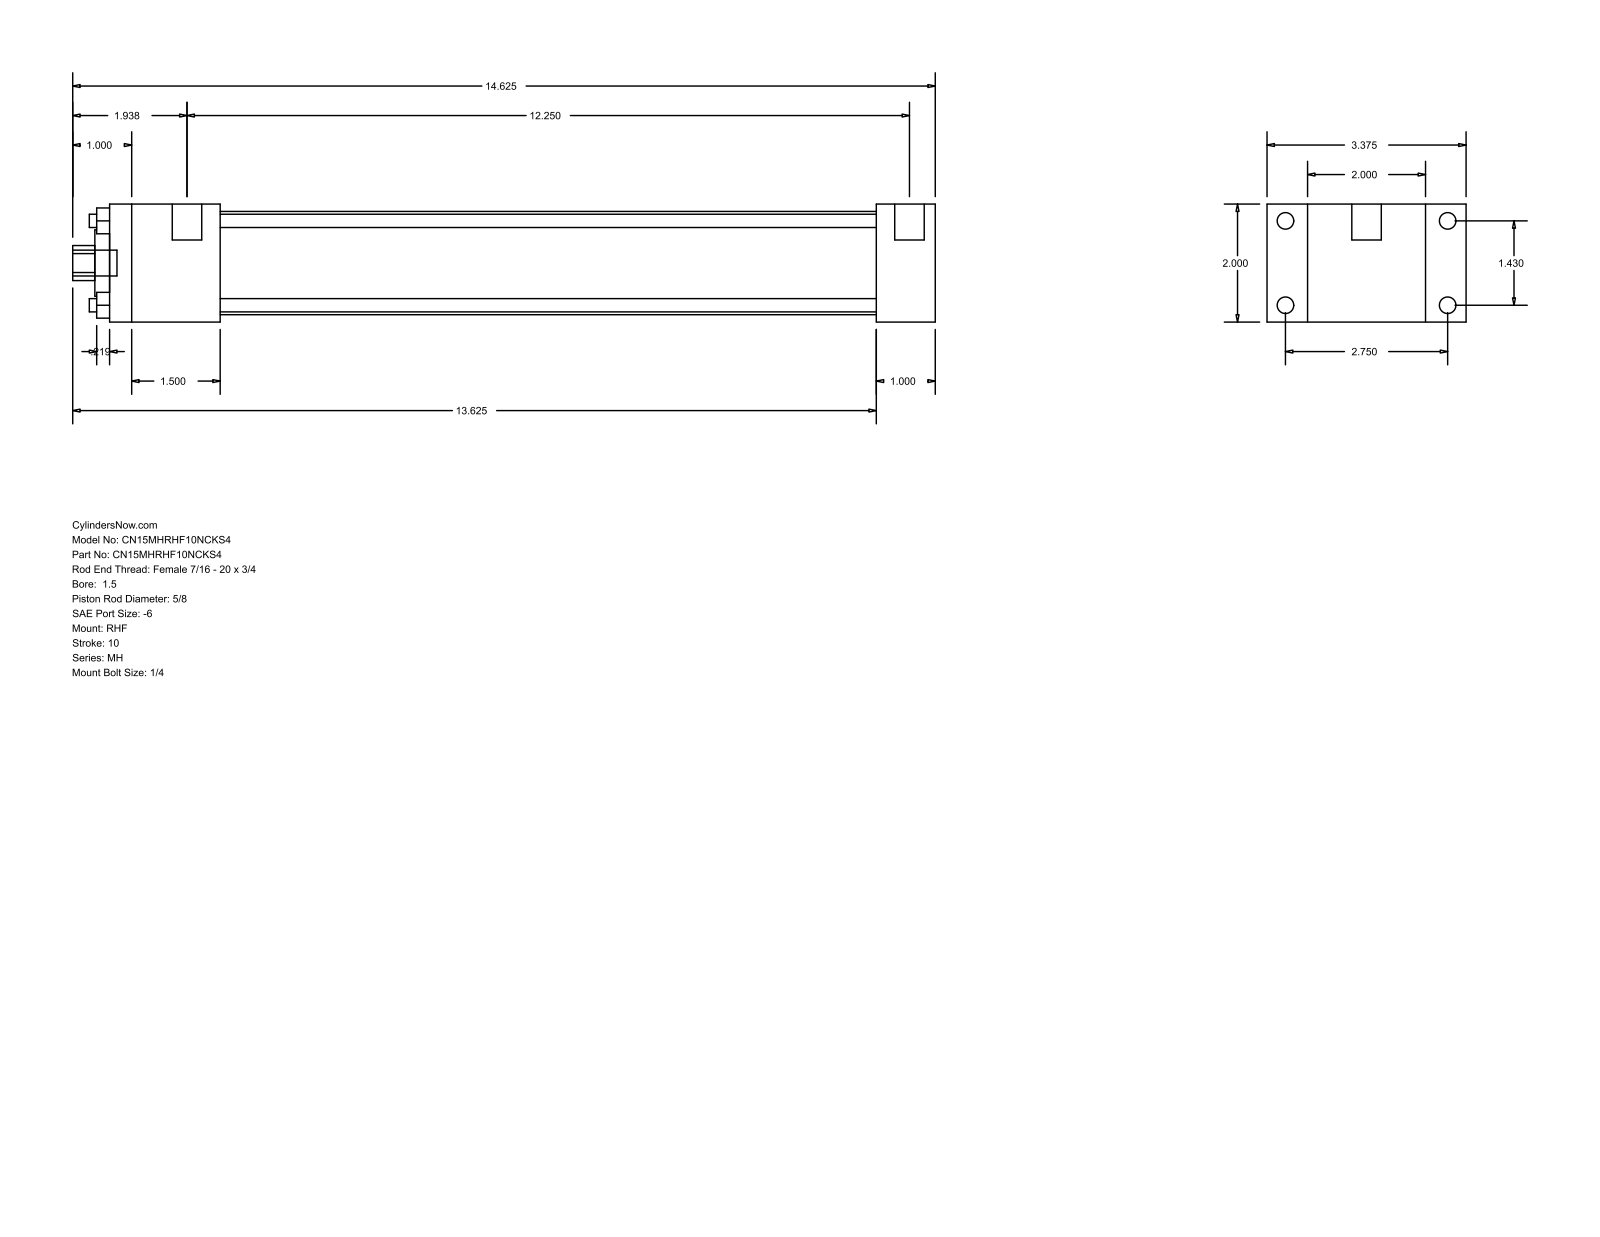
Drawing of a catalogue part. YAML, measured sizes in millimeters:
part_name: "MH_RHF__0150_0.625"
step_written_by: "GSSL Pune (CONFIG_CONTROL_DESIGN)"
units: millimeters
bodies: {solids: 0, faces: 88, planar: 60, cylindrical: 28, other: 0}
overall_size: [371.48, 85.72, 50.8]
round_holes:
  - {diameter: 5.71, count: 4}
  - {diameter: 15.88, count: 1}
  - {diameter: 28.57, count: 1}
  - {diameter: 44.45, count: 1}
round_bosses_or_shafts:
  - {diameter: 7.14, count: 4}
  - {diameter: 5.56, count: 4}
  - {diameter: 12.7, count: 2}
  - {diameter: 11.11, count: 1}
partial_cylinders:
  - {radius: 7.54, count: 1}
face_to_face_distances: [50.8, 17.46, 68.26, 25.41, 330.19, 355.6, 85.72, 47.62, 282.57, 307.98]
hole_center_spacings: [25.68, 36.32, 51.36]
